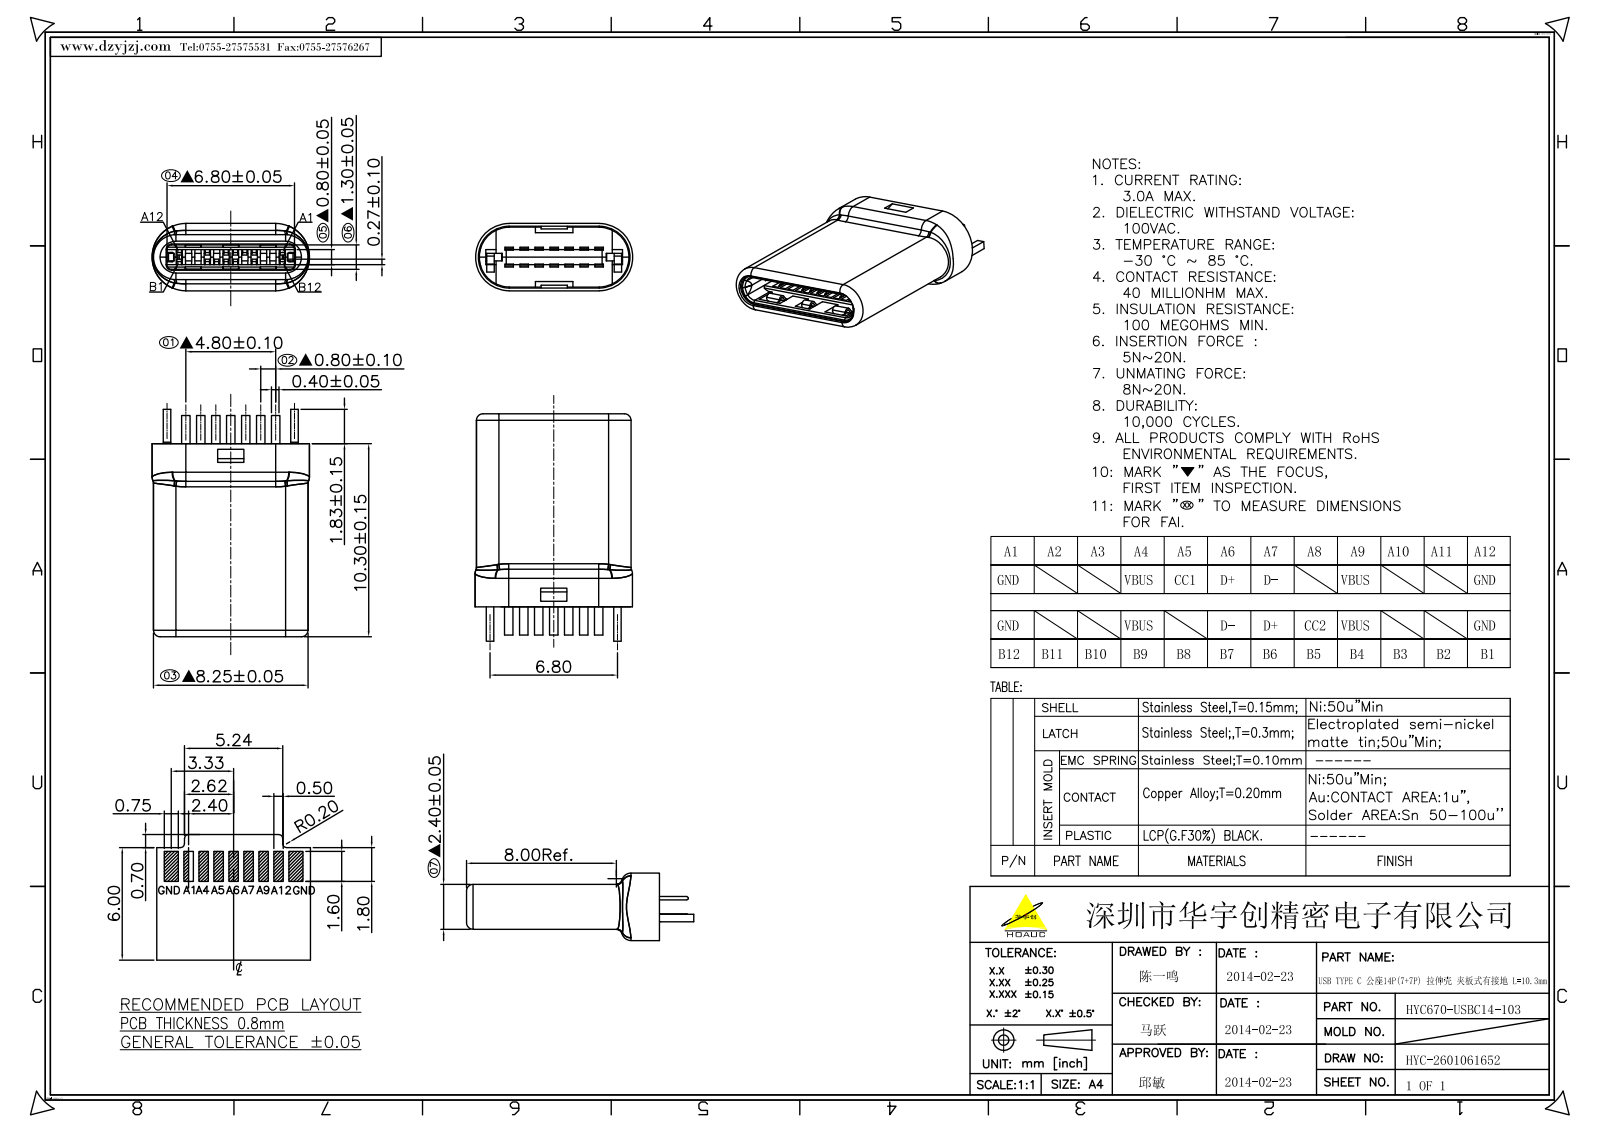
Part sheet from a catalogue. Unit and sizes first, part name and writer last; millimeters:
Units: millimetres
Overall size (bounding box): 12.13 × 8.4 × 3.6
Partial cylindrical surfaces — rounded edges, fillets, slot ends (radius × count): R0.15 ×9, R0.25 ×5, R0.2 ×4, R0.3 ×4, R0.35 ×4, R0.12 ×2, R0.45 ×2, R0.5 ×2
Main face-to-face distances: 0.8, 1.6, 2.4, 0.4, 1.2, 1.05, 0.55, 1.25, 0.6, 2.85
Volume: 171 mm³ · Surface area: 481 mm²
Bodies: 1 solid, 428 faces (296 planar, 78 cylindrical, 54 other)
Part name (STEP PRODUCT): TYPE_C_MODING-10_30
STEP written by: CREO PARAMETRIC BY PTC INC, 2022073 (CONFIG_CONTROL_DESIGN)
